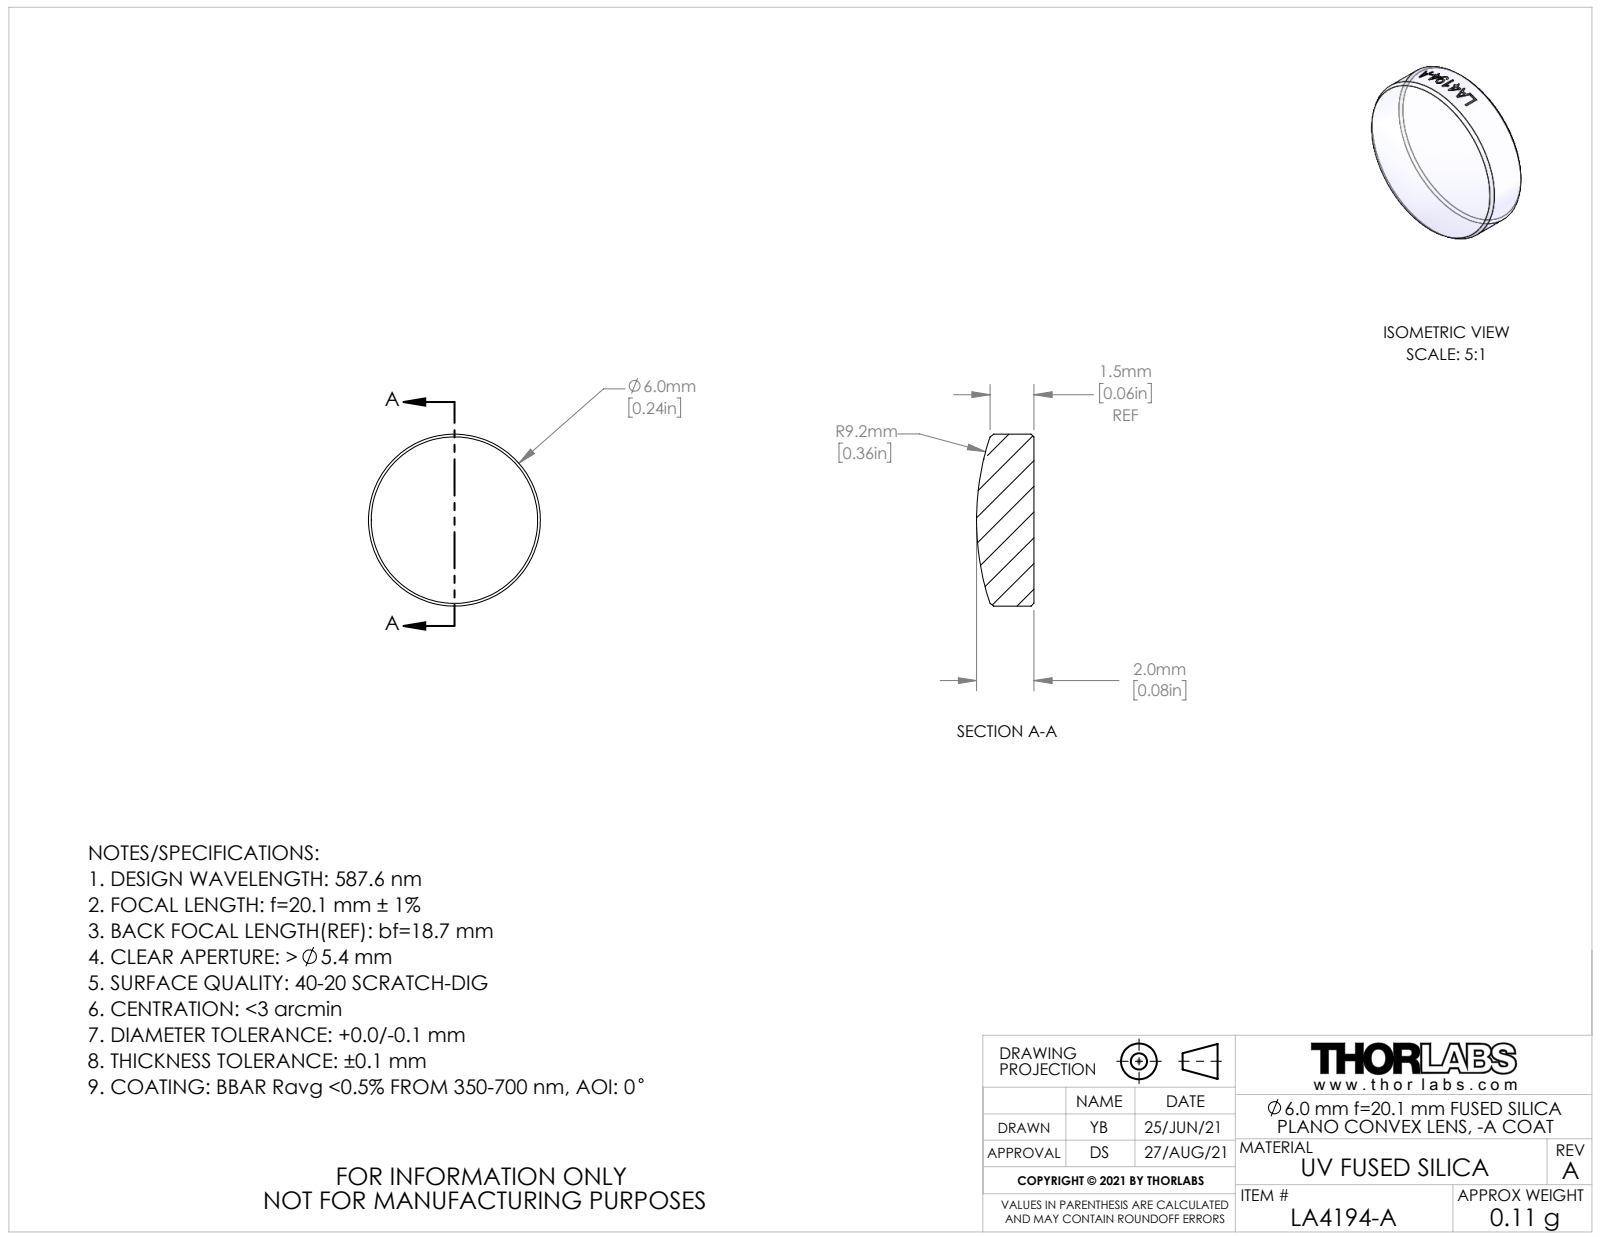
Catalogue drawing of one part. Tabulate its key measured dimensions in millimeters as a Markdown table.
| quantity | value |
| --- | --- |
| part name | CTN017509-E0W; CTN017552 |
| STEP written by | SolidWorks 2018 (AUTOMOTIVE_DESIGN) |
| units | millimeters |
| bodies | 1 solid, 22 faces (1 planar, 15 cylindrical, 6 other) |
| overall size | 6 × 6 × 2 |
| volume | 49 mm³ |
| surface area | 84 mm² |
| round bosses / shafts (diameter × count) | 6 × 1 |
